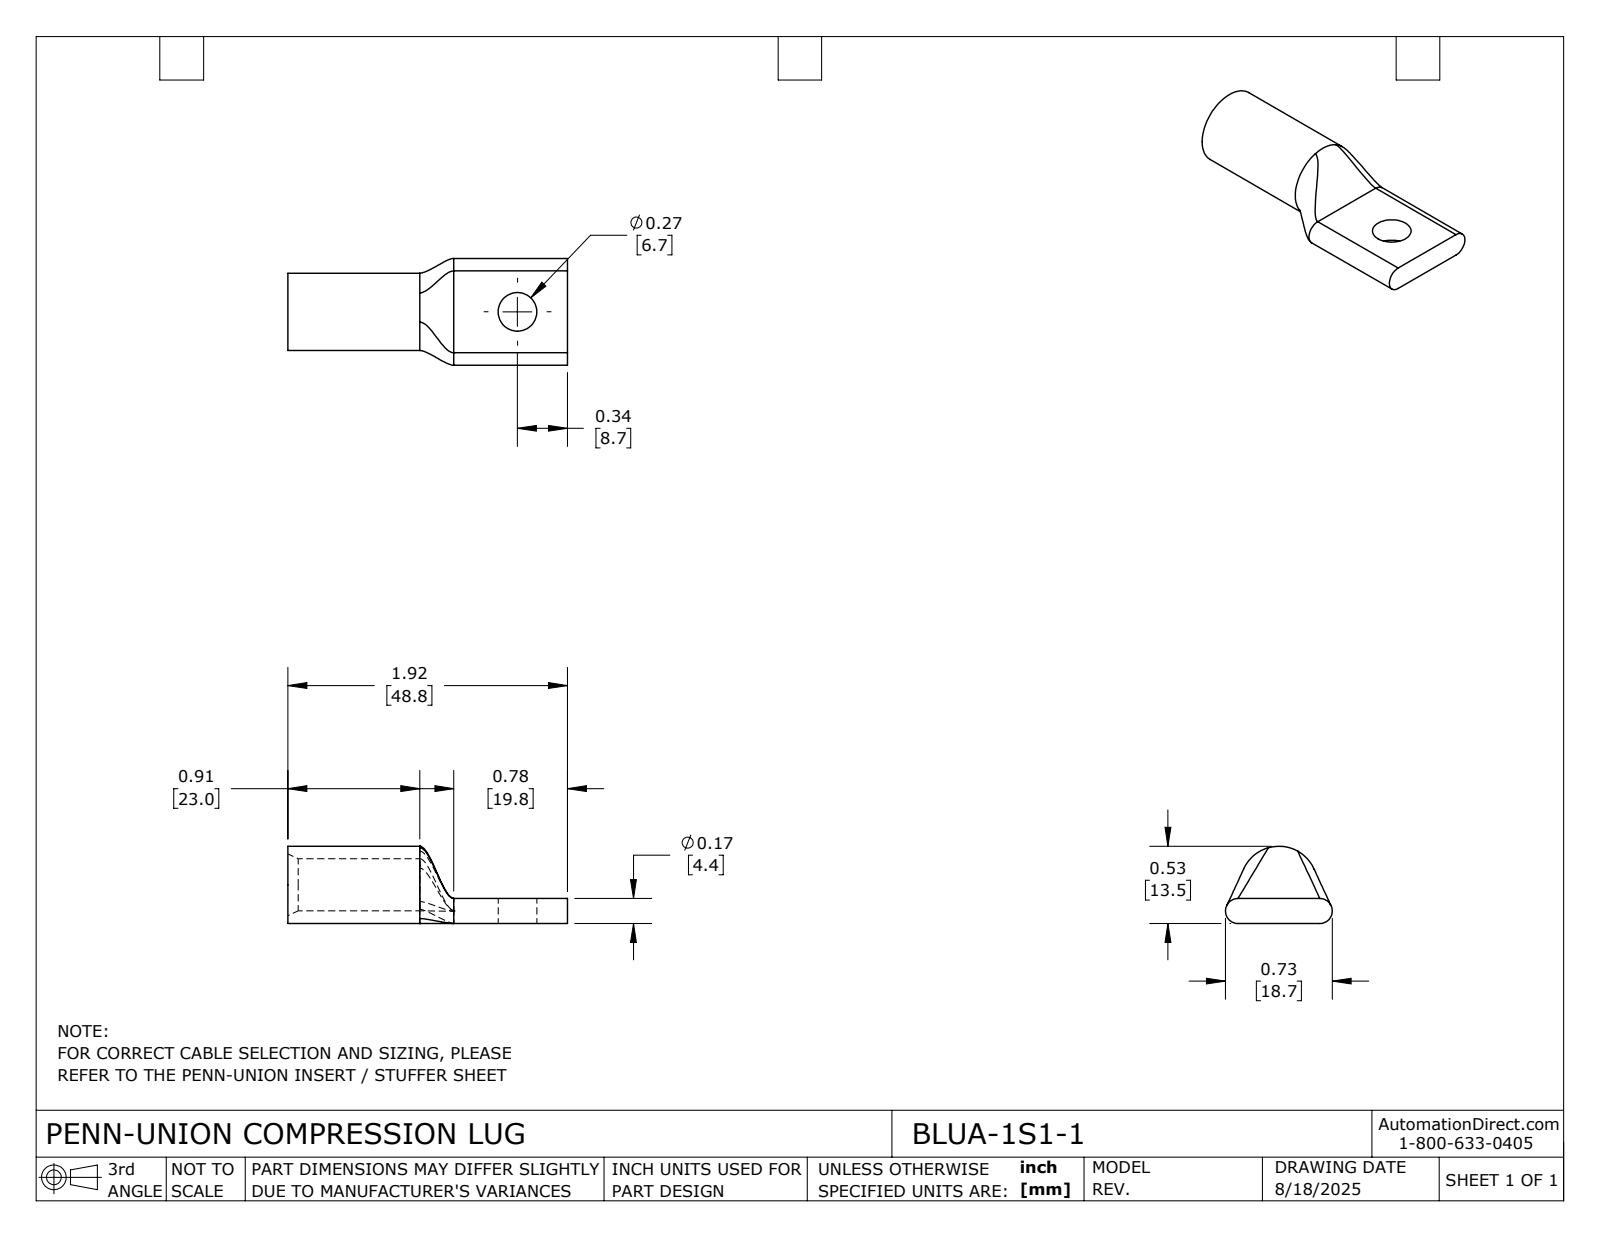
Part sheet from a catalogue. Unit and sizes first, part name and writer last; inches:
Units: inches
Overall size (bounding box): 1.922 × 0.734 × 0.531
Round holes (diameter × count): ⌀0.266 ×1, ⌀0.358 ×1
Round bosses / shafts (diameter × count): ⌀0.531 ×1
Partial cylindrical surfaces — rounded edges, fillets, slot ends (radius × count): R0.086 ×2
Main face-to-face distances: 0.172, 1.922, 1.141, 0.781
Volume: 0.22 in³ · Surface area: 4.921 in²
Bodies: 1 solid, 24 faces (5 planar, 9 cylindrical, 10 other)
Part name (STEP PRODUCT): BLUA-1S1-1
STEP written by: SolidWorks 2024 (CONFIG_CONTROL_DESIGN)
